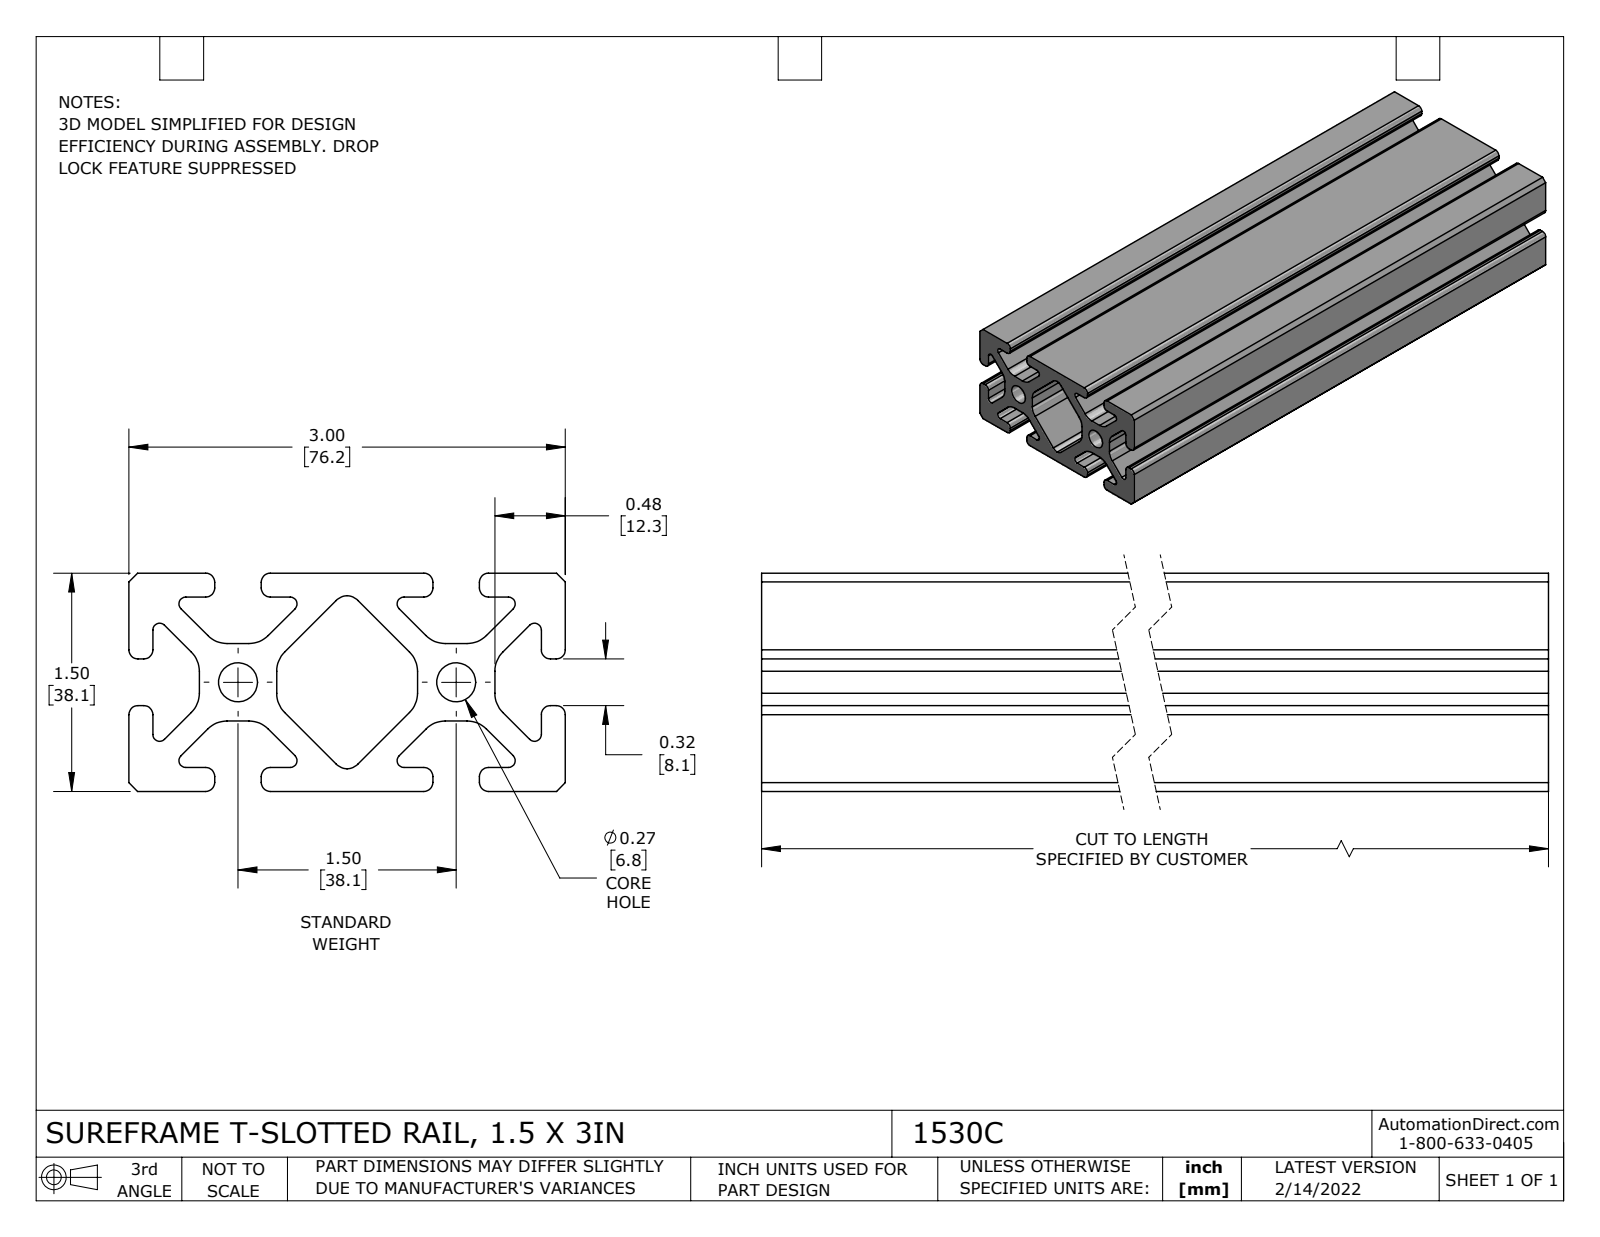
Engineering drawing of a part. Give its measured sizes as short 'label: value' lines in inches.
name: 1530C
written by: SolidWorks 2021 (CONFIG_CONTROL_DESIGN)
unit: in
bodies: 1 solid, 130 faces (64 planar, 66 cylindrical, 0 other)
size: 8 × 3 × 1.5
volume: 17.04 in³; area: 185.8 in²
holes: 2× ⌀0.268
rounds: 16× R0.063, 12× R0.047, 11× R0.187, 8× R0.062, 4× R0.115, 4× R0.187, 1× R0.188
face distances: 1.5, 0.16, 1.061, 0.165, 0.901, 1.335, 1.22, 3, 1.016, 0.852
hole spacings: 1.5
